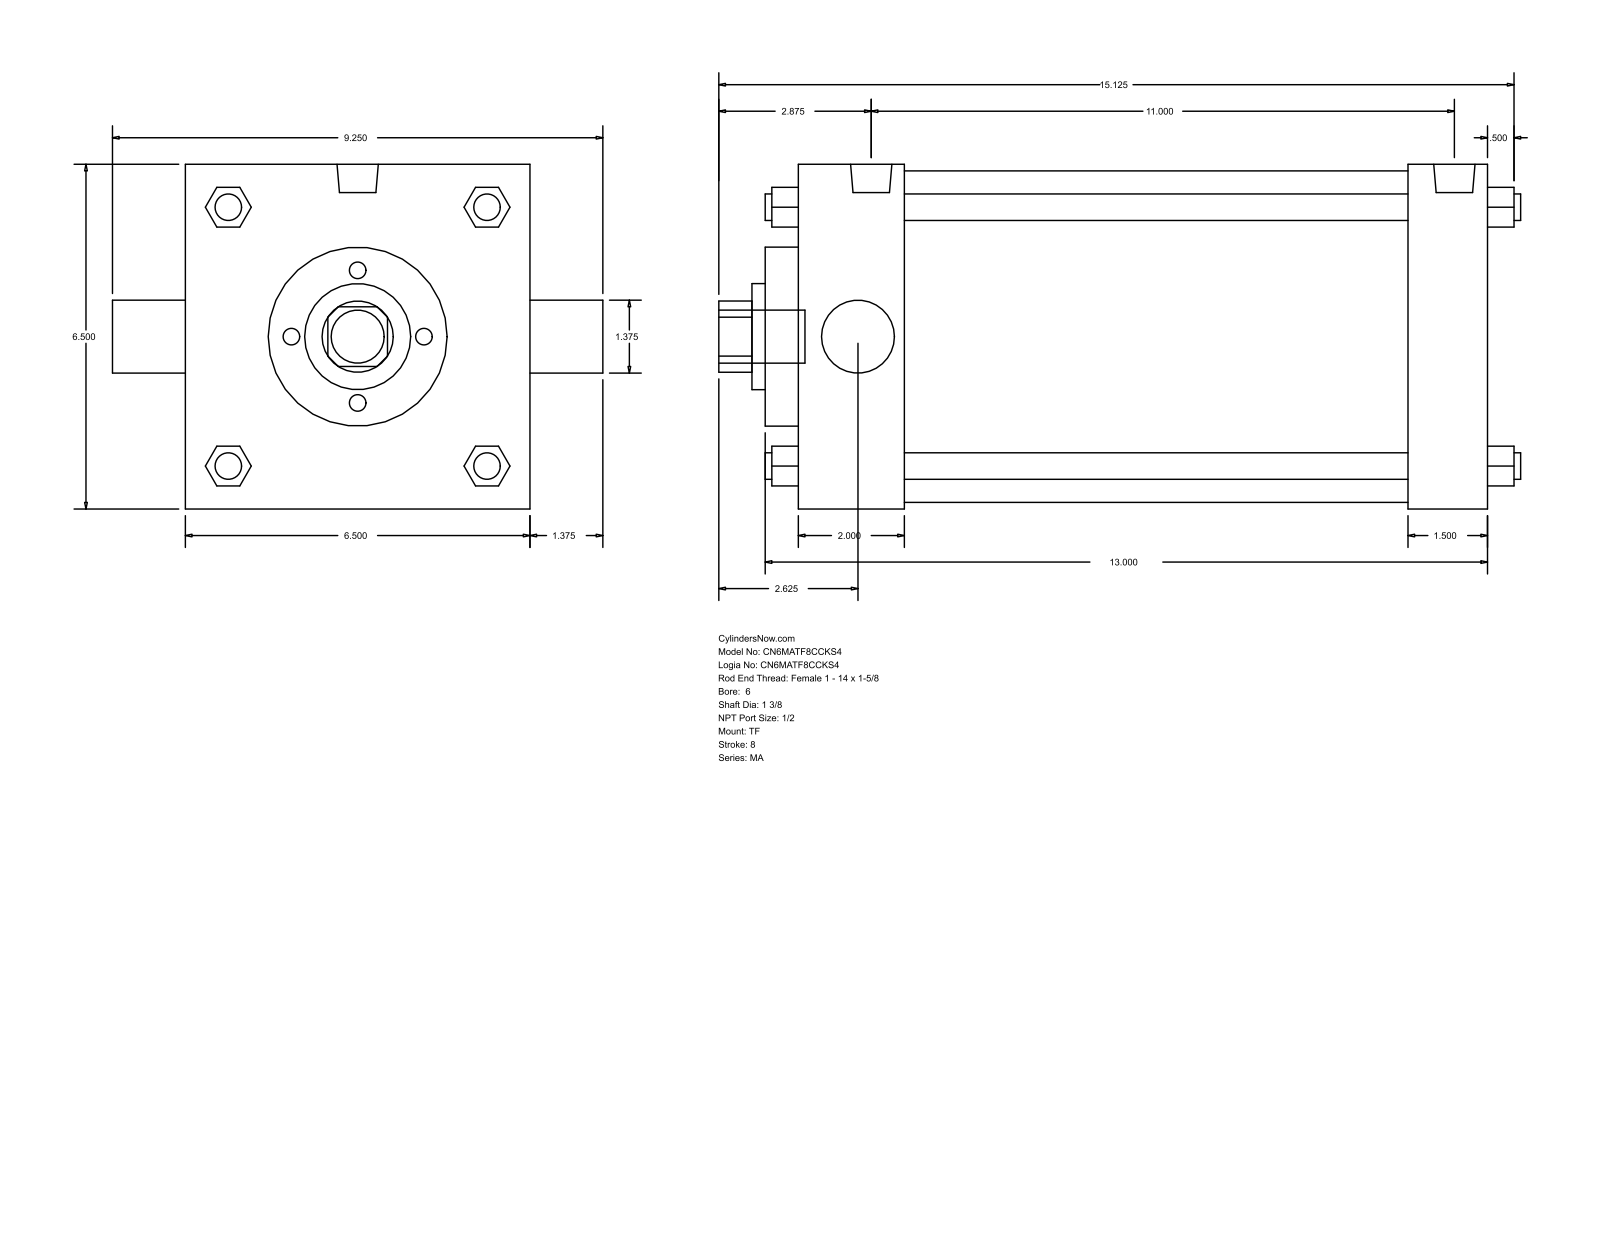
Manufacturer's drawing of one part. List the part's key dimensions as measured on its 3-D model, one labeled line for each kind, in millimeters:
Part name (STEP PRODUCT): MA_TF__0600_1.375
STEP written by: GSSL Pune (CONFIG_CONTROL_DESIGN)
Units: millimetres
Bodies: 0 solids, 122 faces (93 planar, 29 cylindrical, 0 other)
Overall size (bounding box): 384.18 × 234.95 × 165.1
Round holes (diameter × count): ⌀34.92 ×2, ⌀50.8 ×1, ⌀85.72 ×1, ⌀158.75 ×1
Round bosses / shafts (diameter × count): ⌀12.7 ×4, ⌀17.46 ×3, ⌀19.77 ×2, ⌀25.4 ×1
Partial cylindrical surfaces — rounded edges, fillets, slot ends (radius × count): R17.06 ×1
Main face-to-face distances: 165.1, 333.38, 50.8, 295.28, 38.1, 282.58, 244.48, 15.87, 66.67, 311.15
